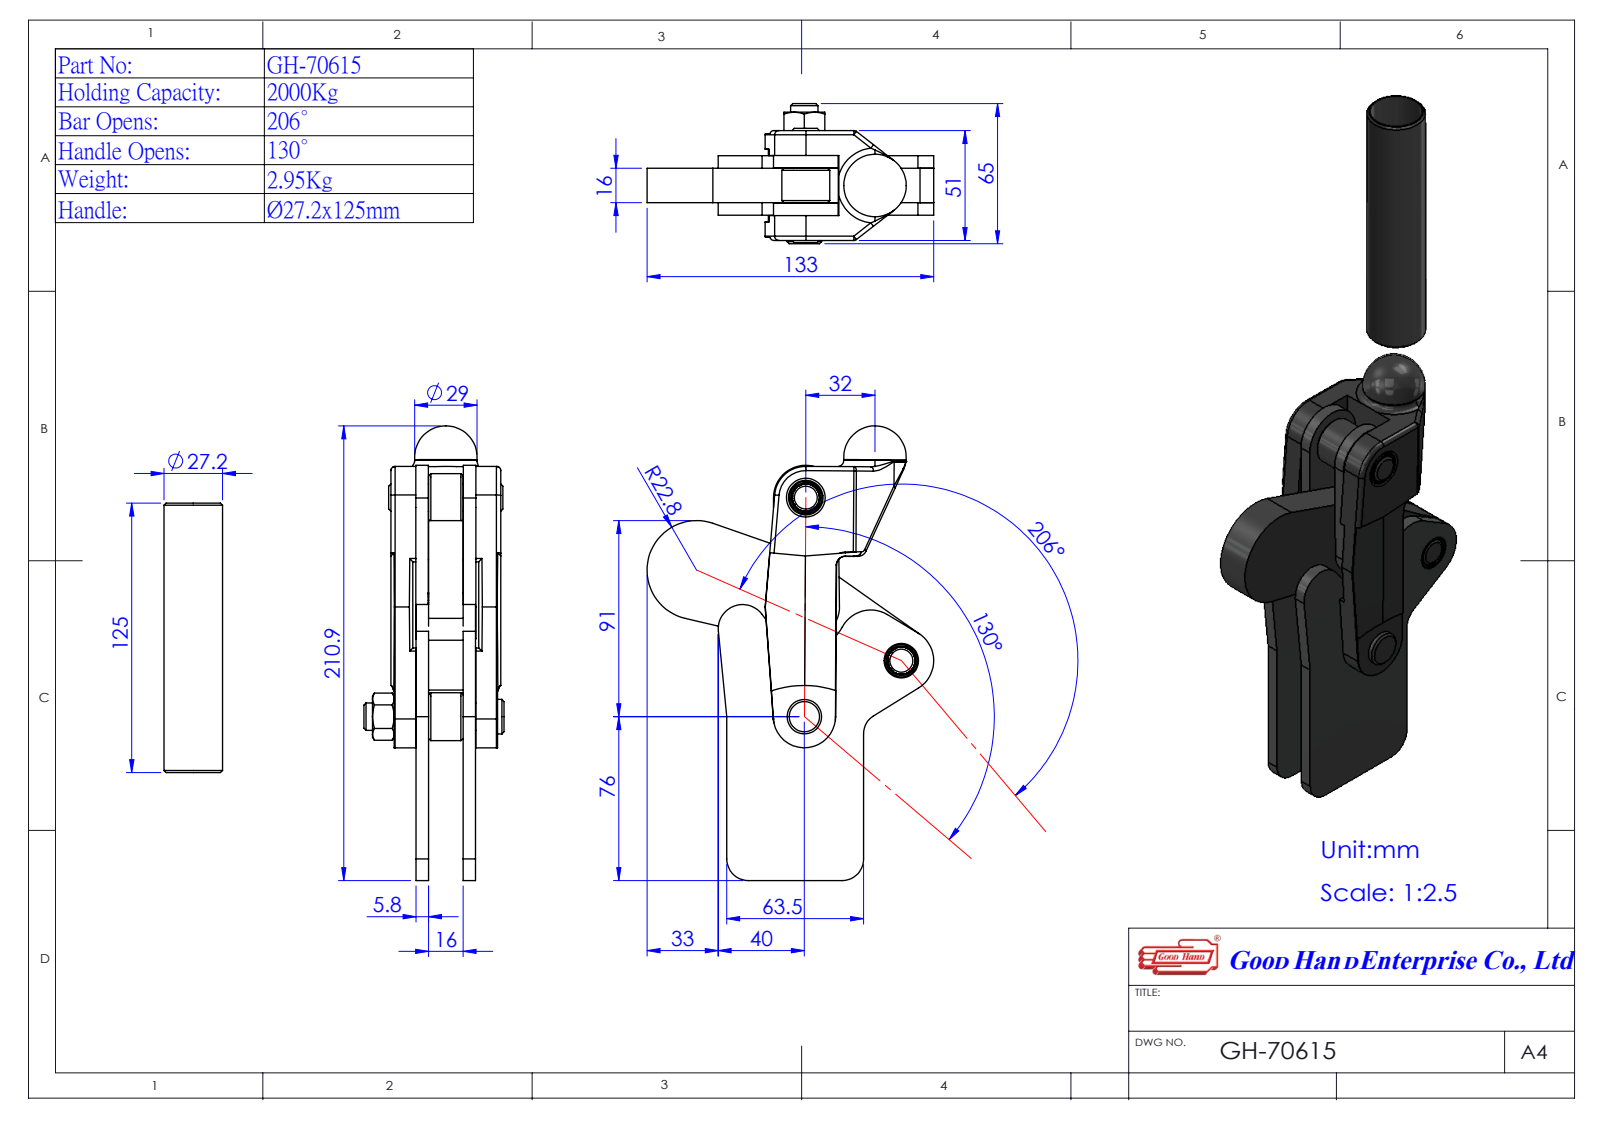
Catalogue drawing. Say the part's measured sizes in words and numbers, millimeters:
The part is named "17060501-1^GH-70615(簡化)-1; Group1^GH-70615(簡化)-1; Group3^GH-70615(簡化)-1; Group5^GH-70615(簡化)-1 (+2 more)". Its 3-D file was written by "SolidWorks 2016 (AUTOMOTIVE_DESIGN)". It is 5 solids with 152 faces: 64 planar, 70 cylindrical and 18 other. Overall it measures 335.96 by 133.21 by 65 millimeters. Its volume is 384 341 cubic millimeters and its surface area 120 968 square millimeters. Round holes: 3 of diameter 12.7, 1 of diameter 22.2. Round bosses or shafts: 1 of diameter 27.2, 1 of diameter 22.2, 1 of diameter 16, 1 of diameter 12.7, 1 of diameter 12.66. Partial cylindrical surfaces (rounded edges, fillets, slot ends): 4 of radius 14.5, 4 of radius 15, 2 of radius 4, 2 of radius 10, 1 of radius 9.5, 1 of radius 11.3, 1 of radius 18.42, 1 of radius 21.99. The main face-to-face distances are 5.8, 21.8, 16, 27.6, 21.92, 21.93, 11.7, 17.5, 33.5, 39.3. The hole center spacings are 50.4, 50.72, 51.96.
